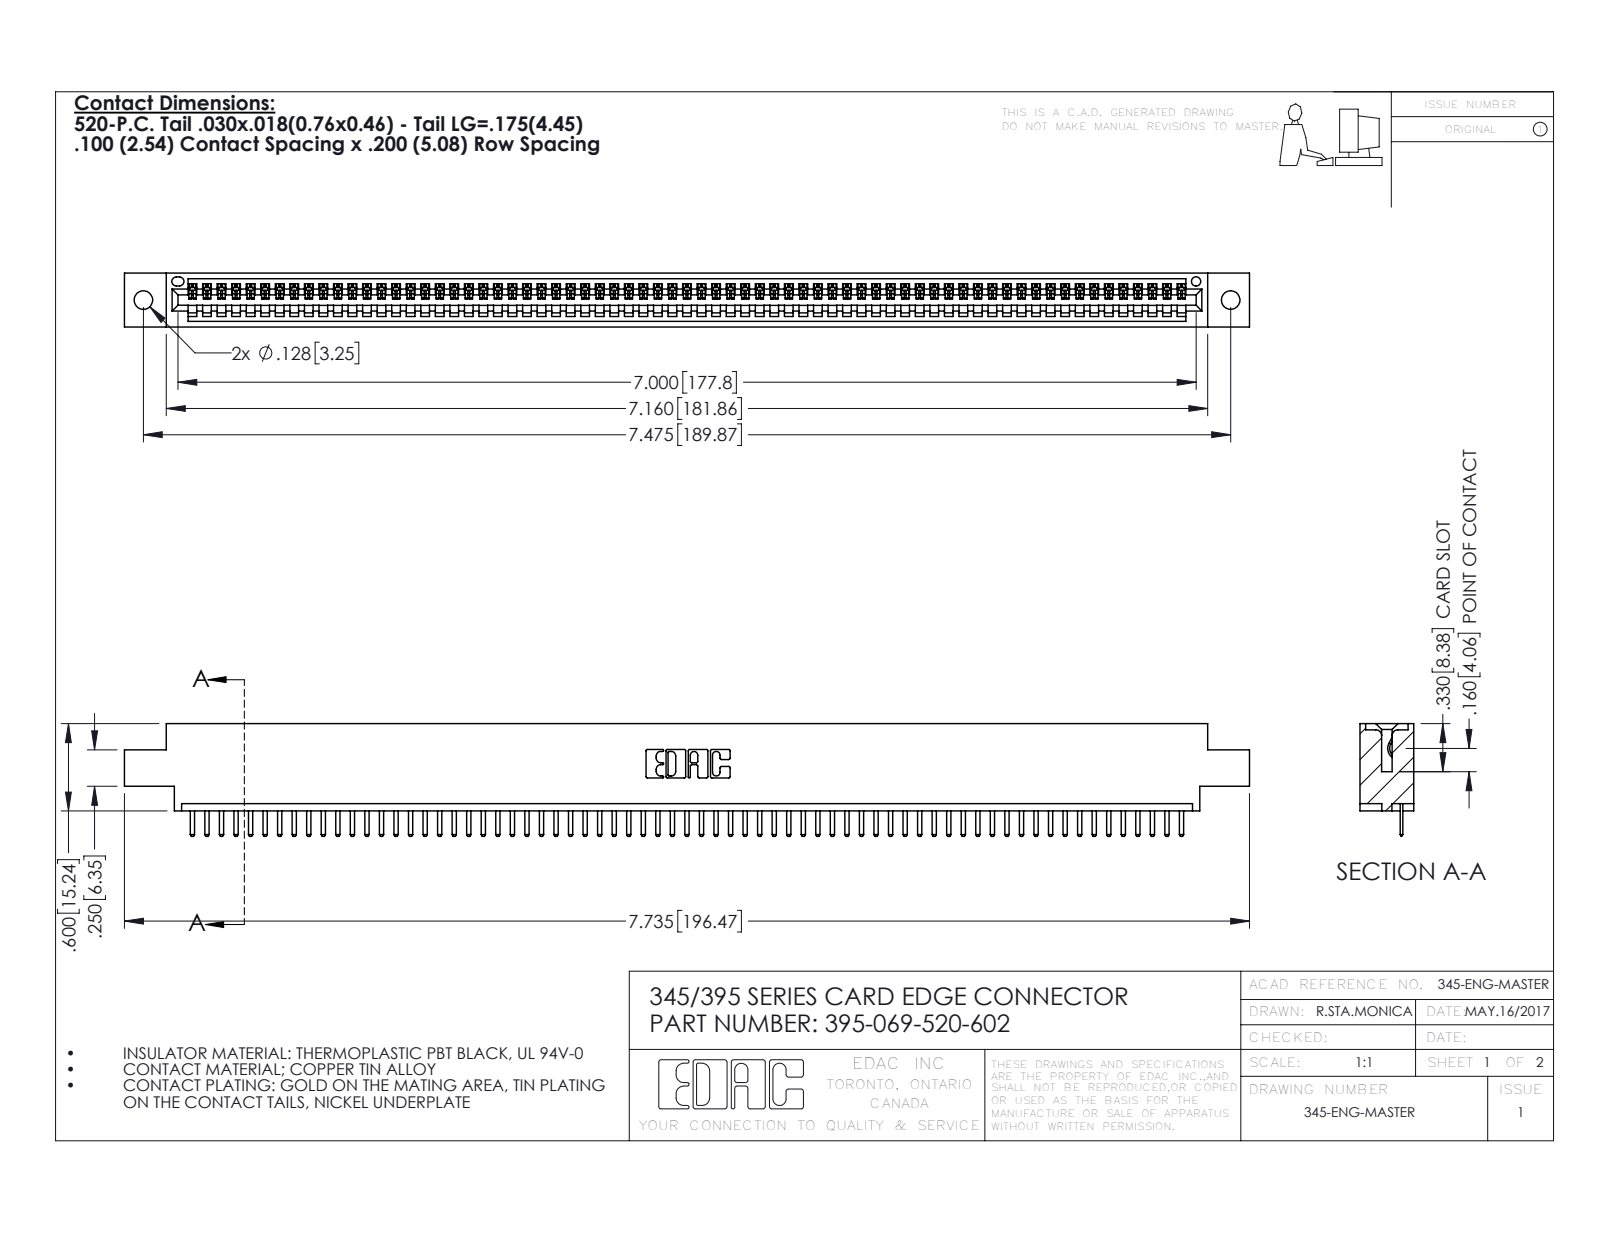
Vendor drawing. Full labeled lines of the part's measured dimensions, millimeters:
Part name (STEP PRODUCT): 345 Part_0.170 Offset - 0.128 Dia; 395-069-520-602; 345-292-001_345-293-120
STEP written by: SolidWorks 2016 (CONFIG_CONTROL_DESIGN)
Units: millimetres
Bodies: 70 solids, 4408 faces (2982 planar, 1426 cylindrical, 0 other)
Overall size (bounding box): 196.5 × 19.7 × 9.4
Volume: 18 530 mm³ · Surface area: 24 200 mm²
Round holes (diameter × count): ⌀3.3 ×2, ⌀1.6 ×1
Partial cylindrical surfaces — rounded edges, fillets, slot ends (radius × count): R0.3 ×140, R0.2 ×138, R0.3 ×22, R0.2 ×6, R0.8 ×6, R0.7 ×3, R0.8 ×2, R1 ×2
Main face-to-face distances: 7.6, 1.8, 9.4, 5.1, 2.5, 6.9, 0.6, 5.7, 1.8, 4.4
Hole centre spacings: 6.9, 183.9, 189.9
